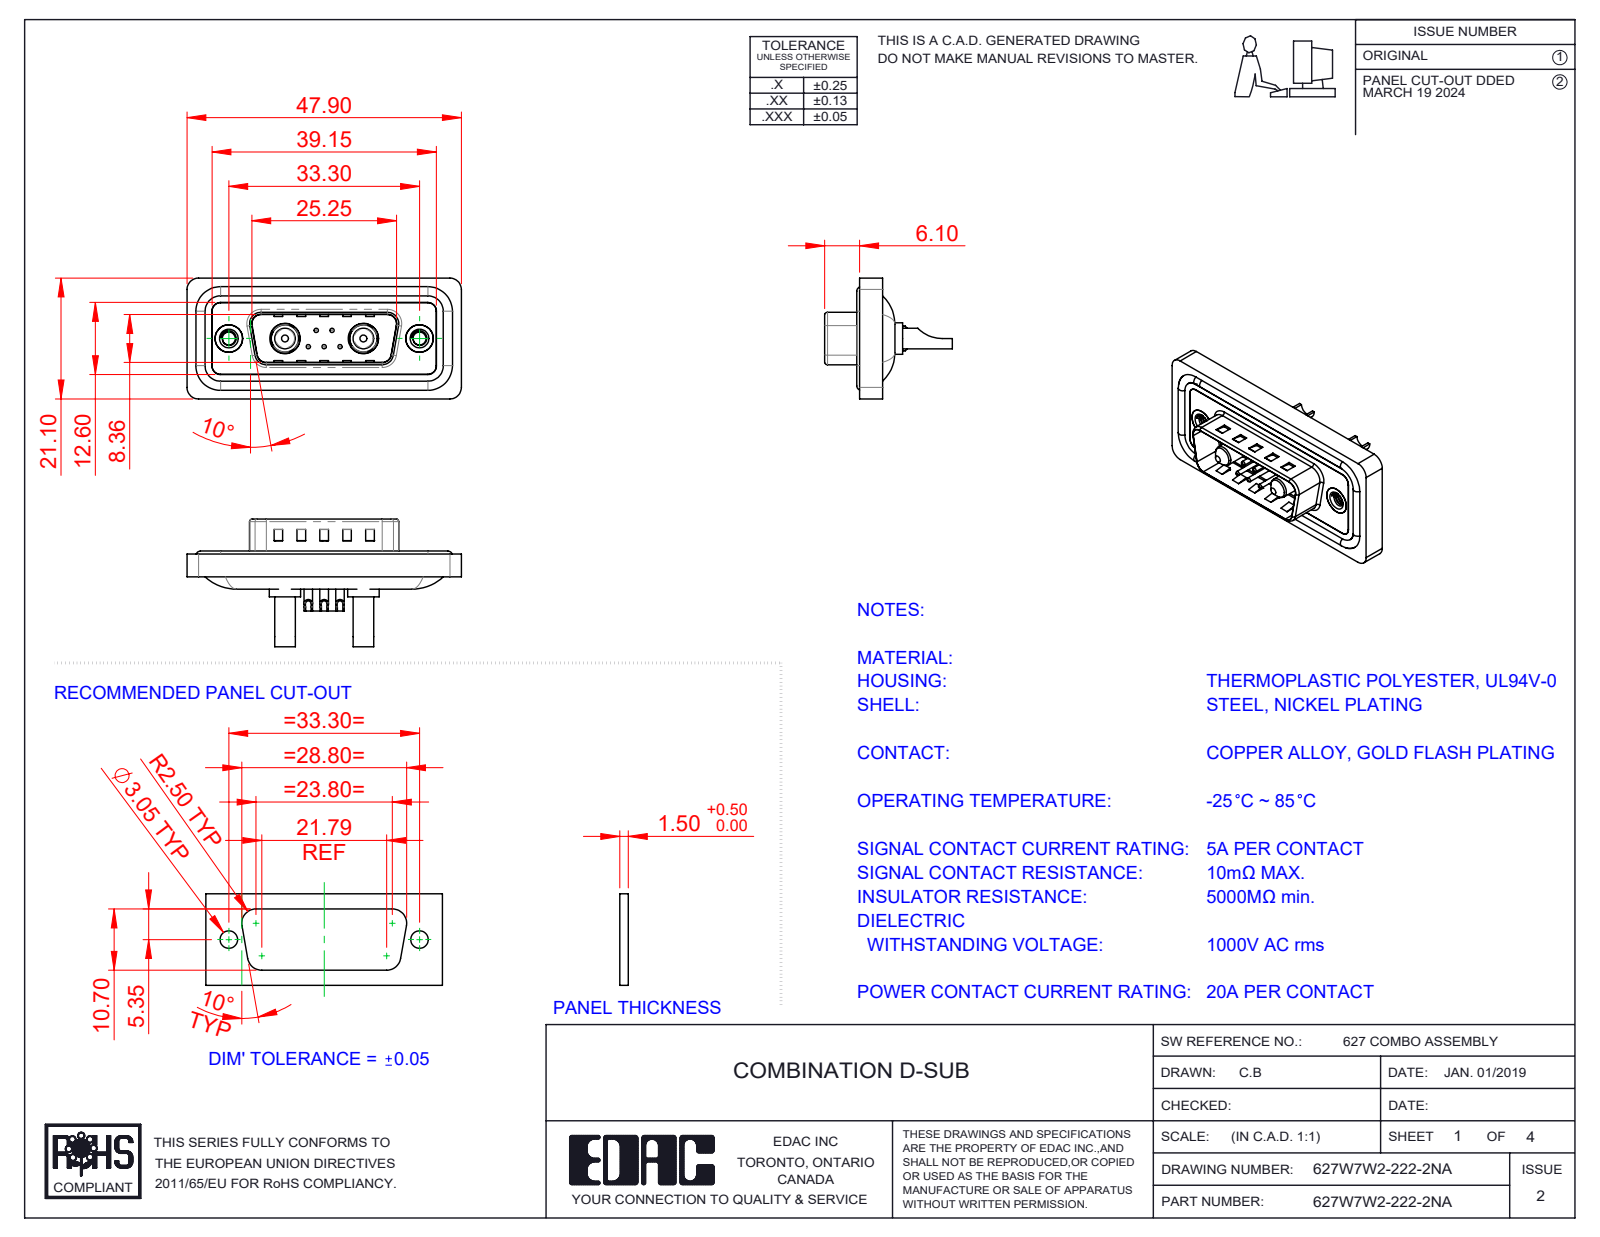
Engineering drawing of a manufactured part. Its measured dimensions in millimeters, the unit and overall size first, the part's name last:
Units: millimetres
Overall size (bounding box): 47.9 × 22.3 × 21.1
Round holes (diameter × count): ⌀0.75 ×5, ⌀1 ×5, ⌀1.6 ×5, ⌀2 ×5, ⌀2.26 ×2, ⌀2.7 ×2, ⌀4 ×2, ⌀4.8 ×2, ⌀4.85 ×2, ⌀5 ×2, ⌀5.3 ×2
Round bosses / shafts (diameter × count): ⌀1.5 ×5, ⌀1.6 ×4, ⌀5.5 ×2, ⌀5.2 ×2, ⌀4.9 ×2, ⌀4.75 ×2, ⌀3.75 ×2, ⌀3.6 ×2
Partial cylindrical surfaces — rounded edges, fillets, slot ends (radius × count): R1.5 ×26, R2 ×20, R0.5 ×8, R1.6 ×8, R1 ×6, R0.25 ×4, R0.6 ×4, R0.65 ×4
Main face-to-face distances: 0.4, 1.1, 1.6, 1.5, 0.5, 3.1, 2.9, 0.82, 9.58, 2.5
Hole centre spacings: 3.16, 2.77, 9.8, 23.5, 4.31, 4.33, 5.03, 5.04
Volume: 5 552 mm³ · Surface area: 8 995 mm²
Bodies: 16 solids, 722 faces (248 planar, 310 cylindrical, 164 other)
Part name (STEP PRODUCT): 627Combo Shell Front_15 Contacts; 627W7W2-222-2NA; 627Combo Housing_7W2; 627Combo Threaded Rivet_A (+5 more)
STEP written by: SolidWorks 2023 (CONFIG_CONTROL_DESIGN)
